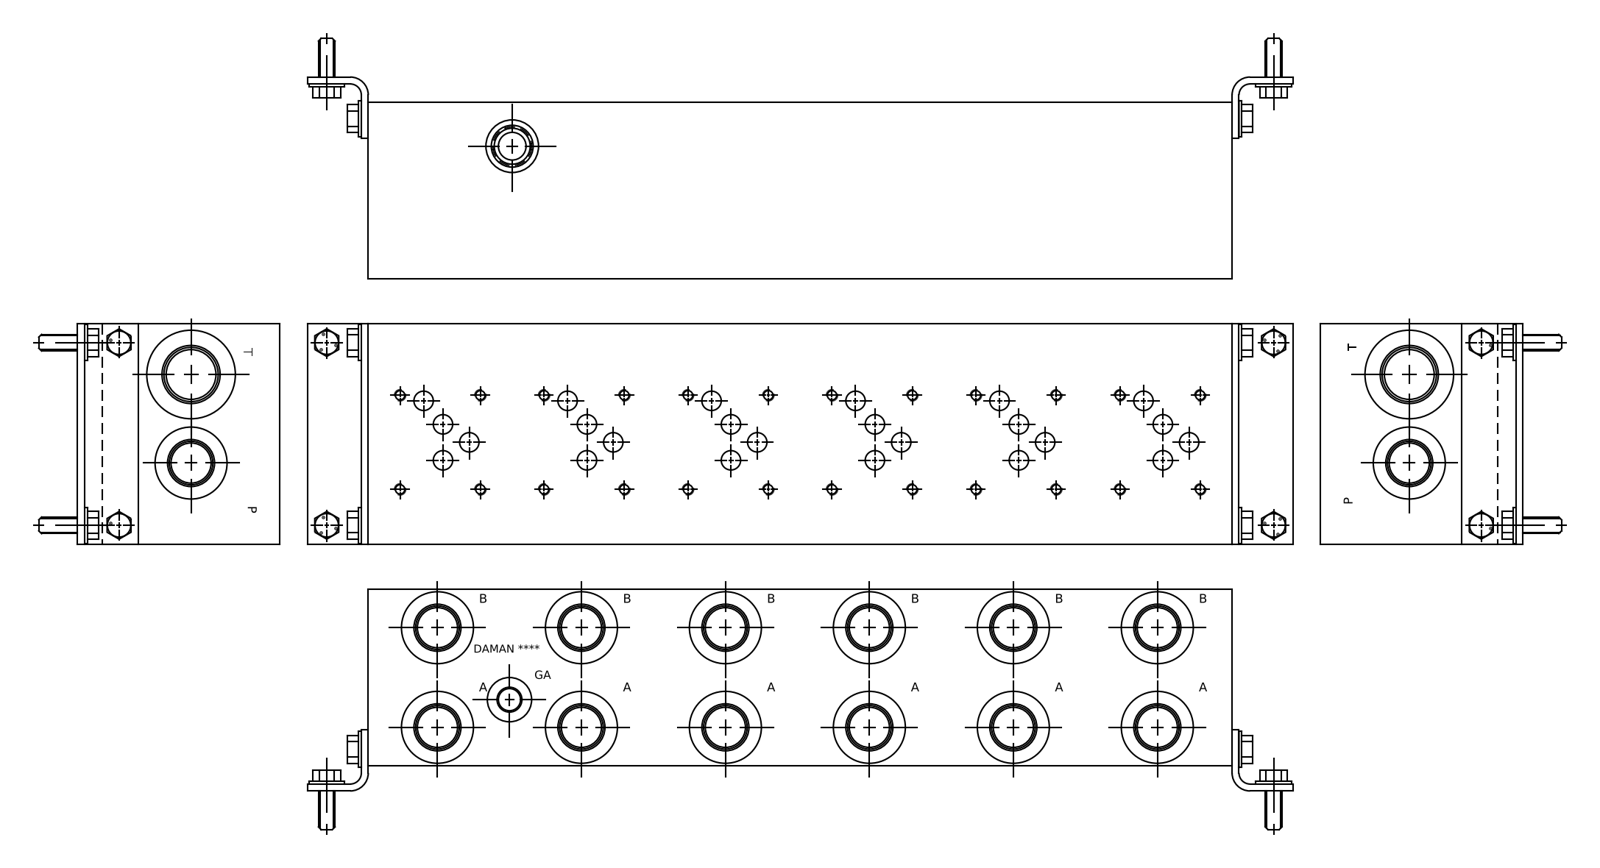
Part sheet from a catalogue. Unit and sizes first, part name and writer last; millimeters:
Units: millimetres
Overall size (bounding box): 495.3 × 127 × 101.6
Round holes (diameter × count): ⌀5.11 ×24, ⌀6.35 ×24, ⌀11.13 ×22, ⌀23.01 ×13, ⌀24.92 ×13, ⌀27.43 ×13, ⌀42.04 ×13, ⌀27 ×12, ⌀7.92 ×2, ⌀9.53 ×2, ⌀11.11 ×2, ⌀26.99 ×2
Main face-to-face distances: 101.6, 127, 0.79, 495.3, 126.21, 494.51, 19.05, 493.72, 19.84, 107.16
Hole centre spacings: 82.55, 165.1, 247.65, 18.27, 68.25, 100.4, 330.2, 85.09
Volume: 6 030 000 mm³ · Surface area: 314 675 mm²
Bodies: 1 solid, 1054 faces (510 planar, 172 cylindrical, 372 other)
Part name (STEP PRODUCT): Part_AD05HP063S_C_3D
STEP written by: Autodesk Inventor 2020 (AUTOMOTIVE_DESIGN)
